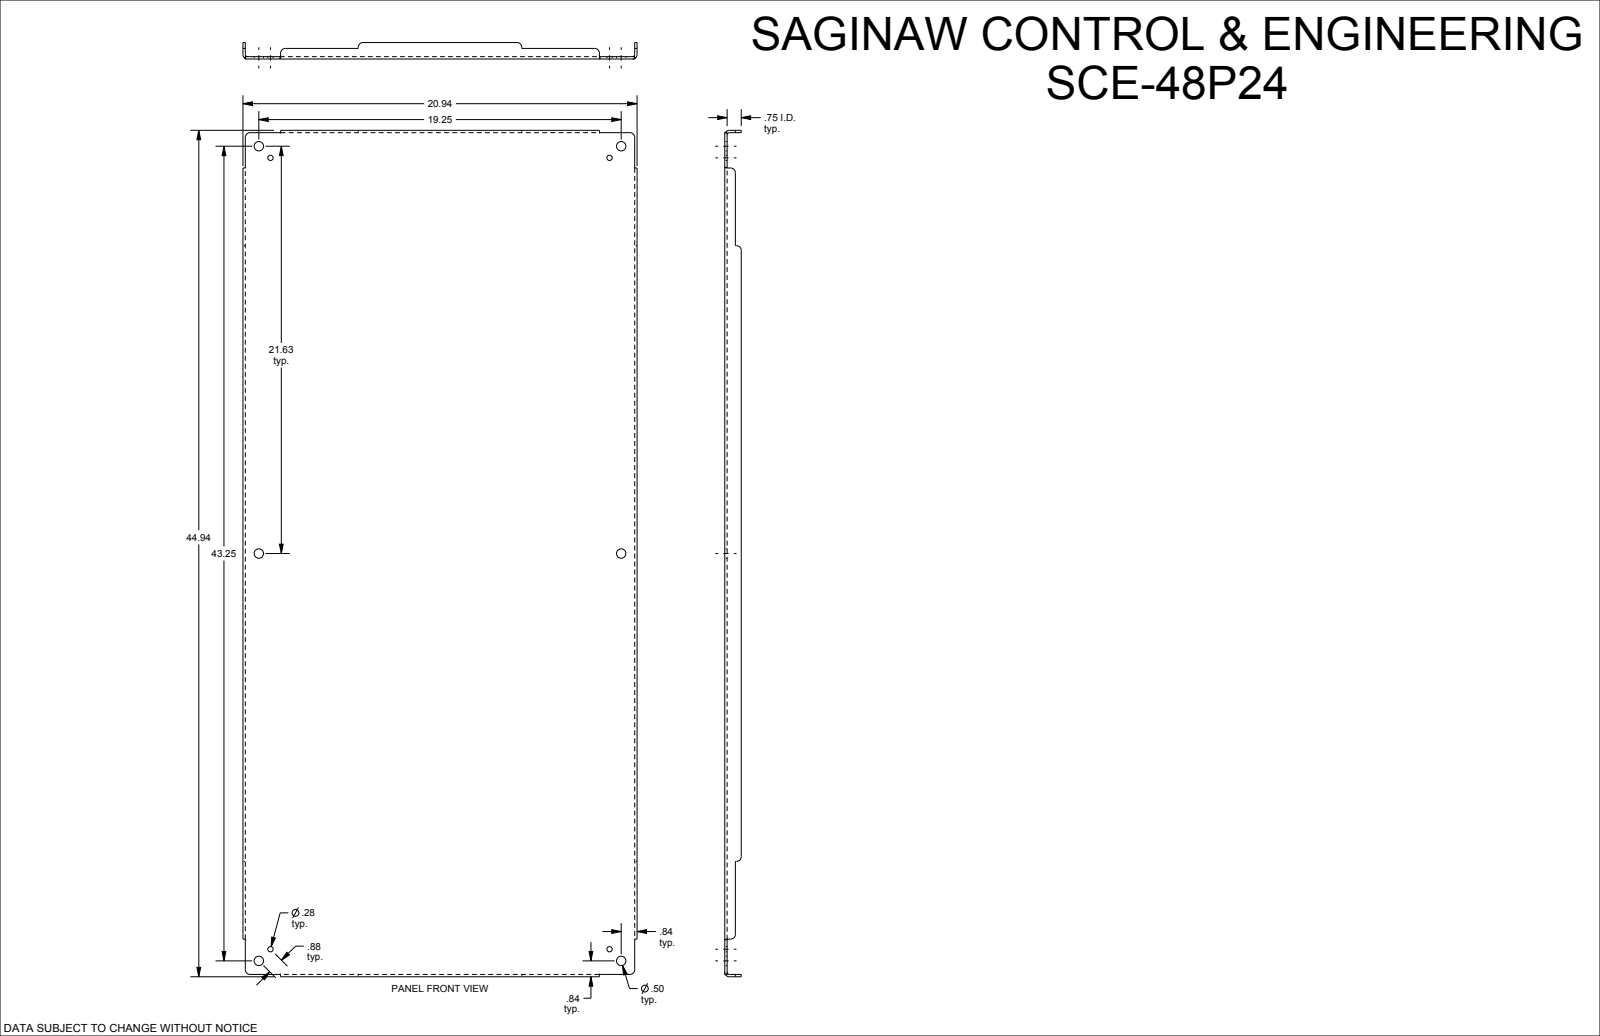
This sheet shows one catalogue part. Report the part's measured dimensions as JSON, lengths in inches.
{"part_name": "SCE-48P24", "step_written_by": "SolidWorks 2019 (CONFIG_CONTROL_DESIGN)", "units": "inches", "bodies": {"solids": 1, "faces": 108, "planar": 46, "cylindrical": 38, "other": 24}, "overall_size": [44.938, 20.938, 0.875], "volume_in3": 125.6, "surface_area_in2": 2029, "round_holes": [[0.5, 6], [0.281, 4]], "partial_cylinders_radius": [[0.25, 12], [0.112, 4], [0.237, 4]], "face_to_face_distances": [0.125, 0.125, 20.813, 20.687, 20.938, 44.813, 0.75, 0.875, 44.687, 44.938], "hole_center_spacings": [0.875, 18.641, 21.015, 21.625, 28.078, 28.951, 42.635, 46.524]}
